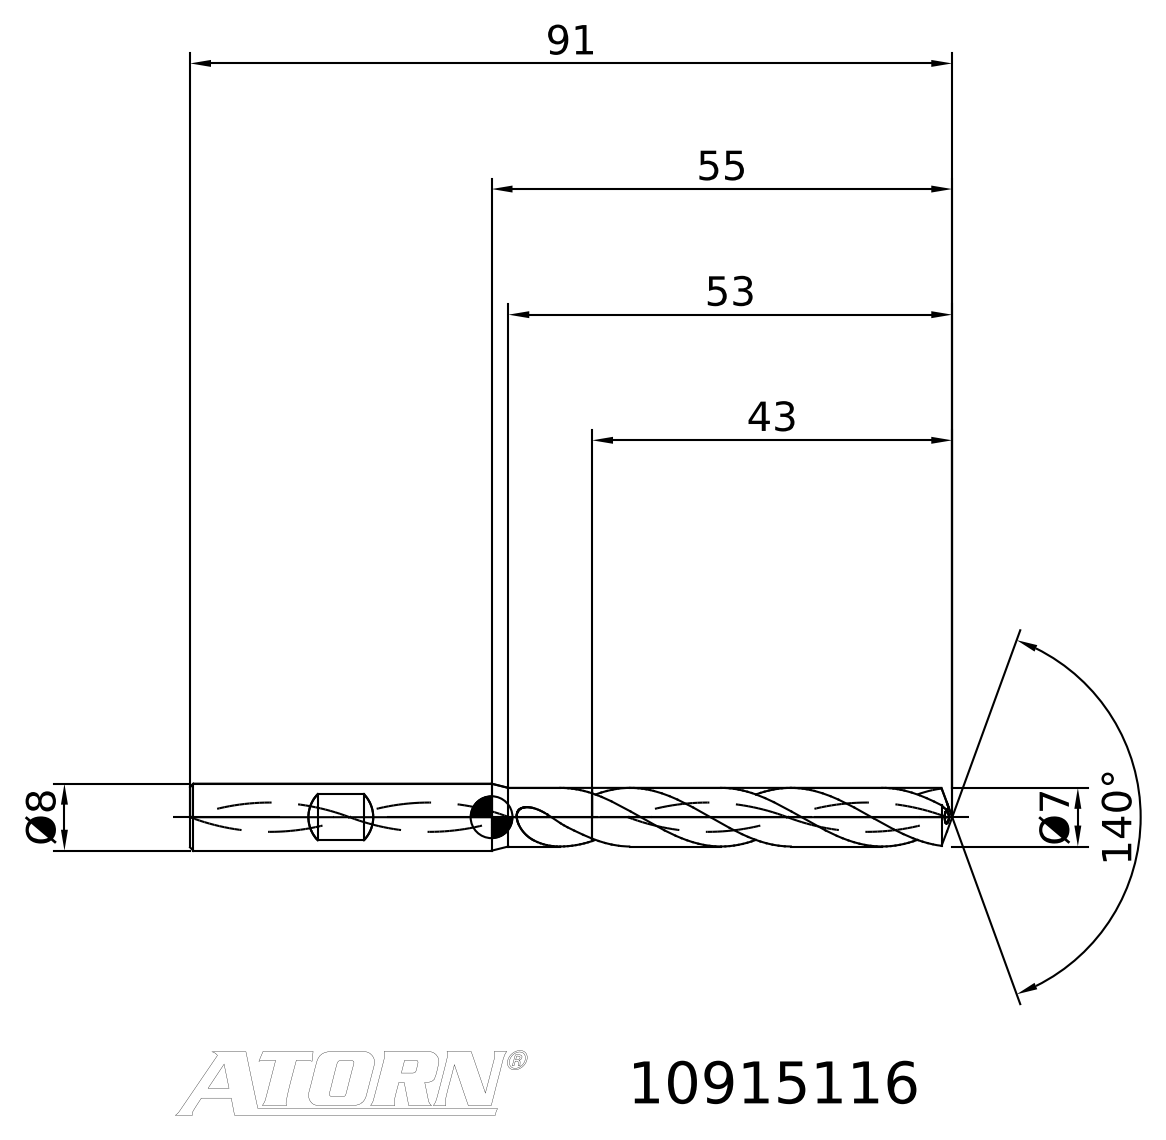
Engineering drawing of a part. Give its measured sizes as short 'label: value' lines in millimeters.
written by: TDM (AUTOMOTIVE_DESIGN)
unit: mm
bodies: 2 solids, 33 faces (8 planar, 0 cylindrical, 25 other)
size: 91 × 8 × 8
volume: 3 227 mm³; area: 2 323 mm²
face distances: 48, 42.04, 90.04
